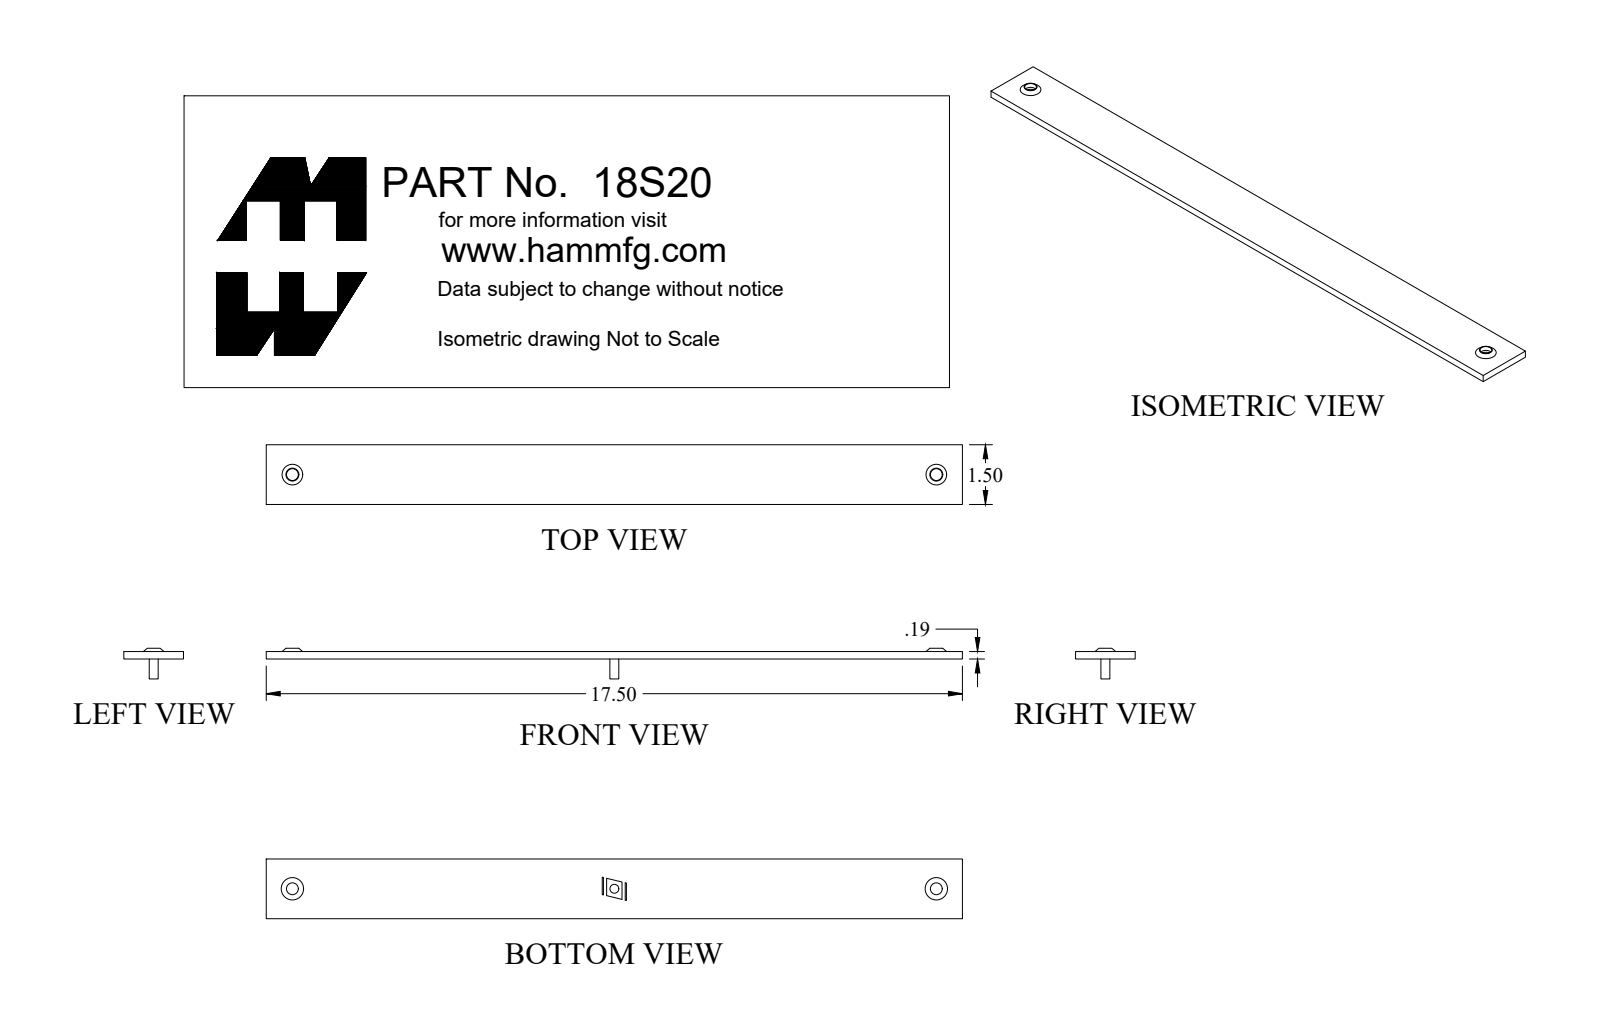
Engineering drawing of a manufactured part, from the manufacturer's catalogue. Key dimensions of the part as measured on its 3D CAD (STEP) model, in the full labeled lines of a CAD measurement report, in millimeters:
Part name (STEP PRODUCT): 18S20_Default
STEP written by: SolidWorks 2018 (CONFIG_CONTROL_DESIGN)
Units: millimetres
Bodies: 1 solid, 20 faces (8 planar, 4 cylindrical, 8 other)
Overall size (bounding box): 444.5 × 38.1 × 6.9
Volume: 80 250 mm³ · Surface area: 38 610 mm²
Round holes (diameter × count): ⌀7.5 ×2
Main face-to-face distances: 4.8, 38.1, 444.5, 6.9, 2.1
Hole centre spacings: 411.2
